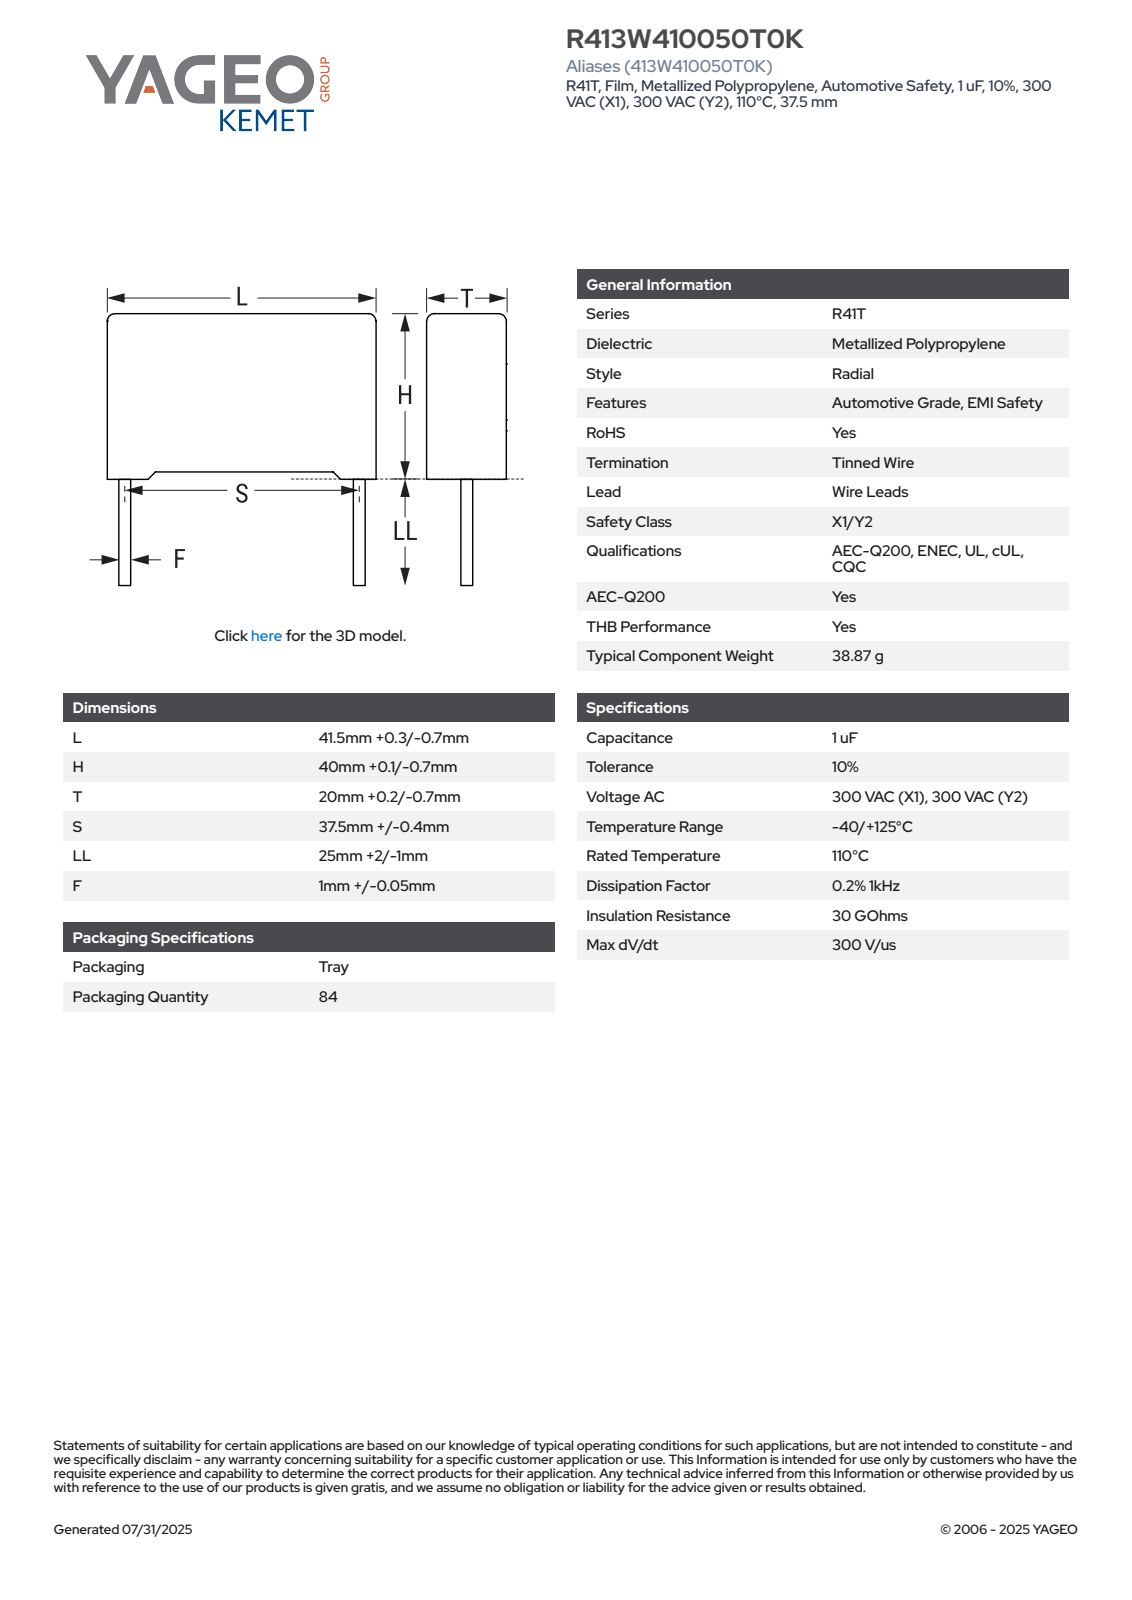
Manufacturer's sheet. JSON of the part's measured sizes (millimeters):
{"part_name": "CFR_RB2_41.5X40X20_L41.8H40.1T20.2S37.5LL27F1.05", "step_written_by": "SolidWorks 2021 (AUTOMOTIVE_DESIGN)", "units": "millimeters", "bodies": {"solids": 4, "faces": 85, "planar": 77, "cylindrical": 8, "other": 0}, "overall_size": [67.1, 41.8, 20.2], "volume_mm3": 32902, "surface_area_mm2": 6904, "round_bosses_or_shafts": [[1.05, 2]], "partial_cylinders_radius": [[0.5, 4]], "face_to_face_distances": [20.2, 41.8, 38.72, 0.63, 39.35, 0.75, 1.38, 40.1, 1.39, 20.21]}
